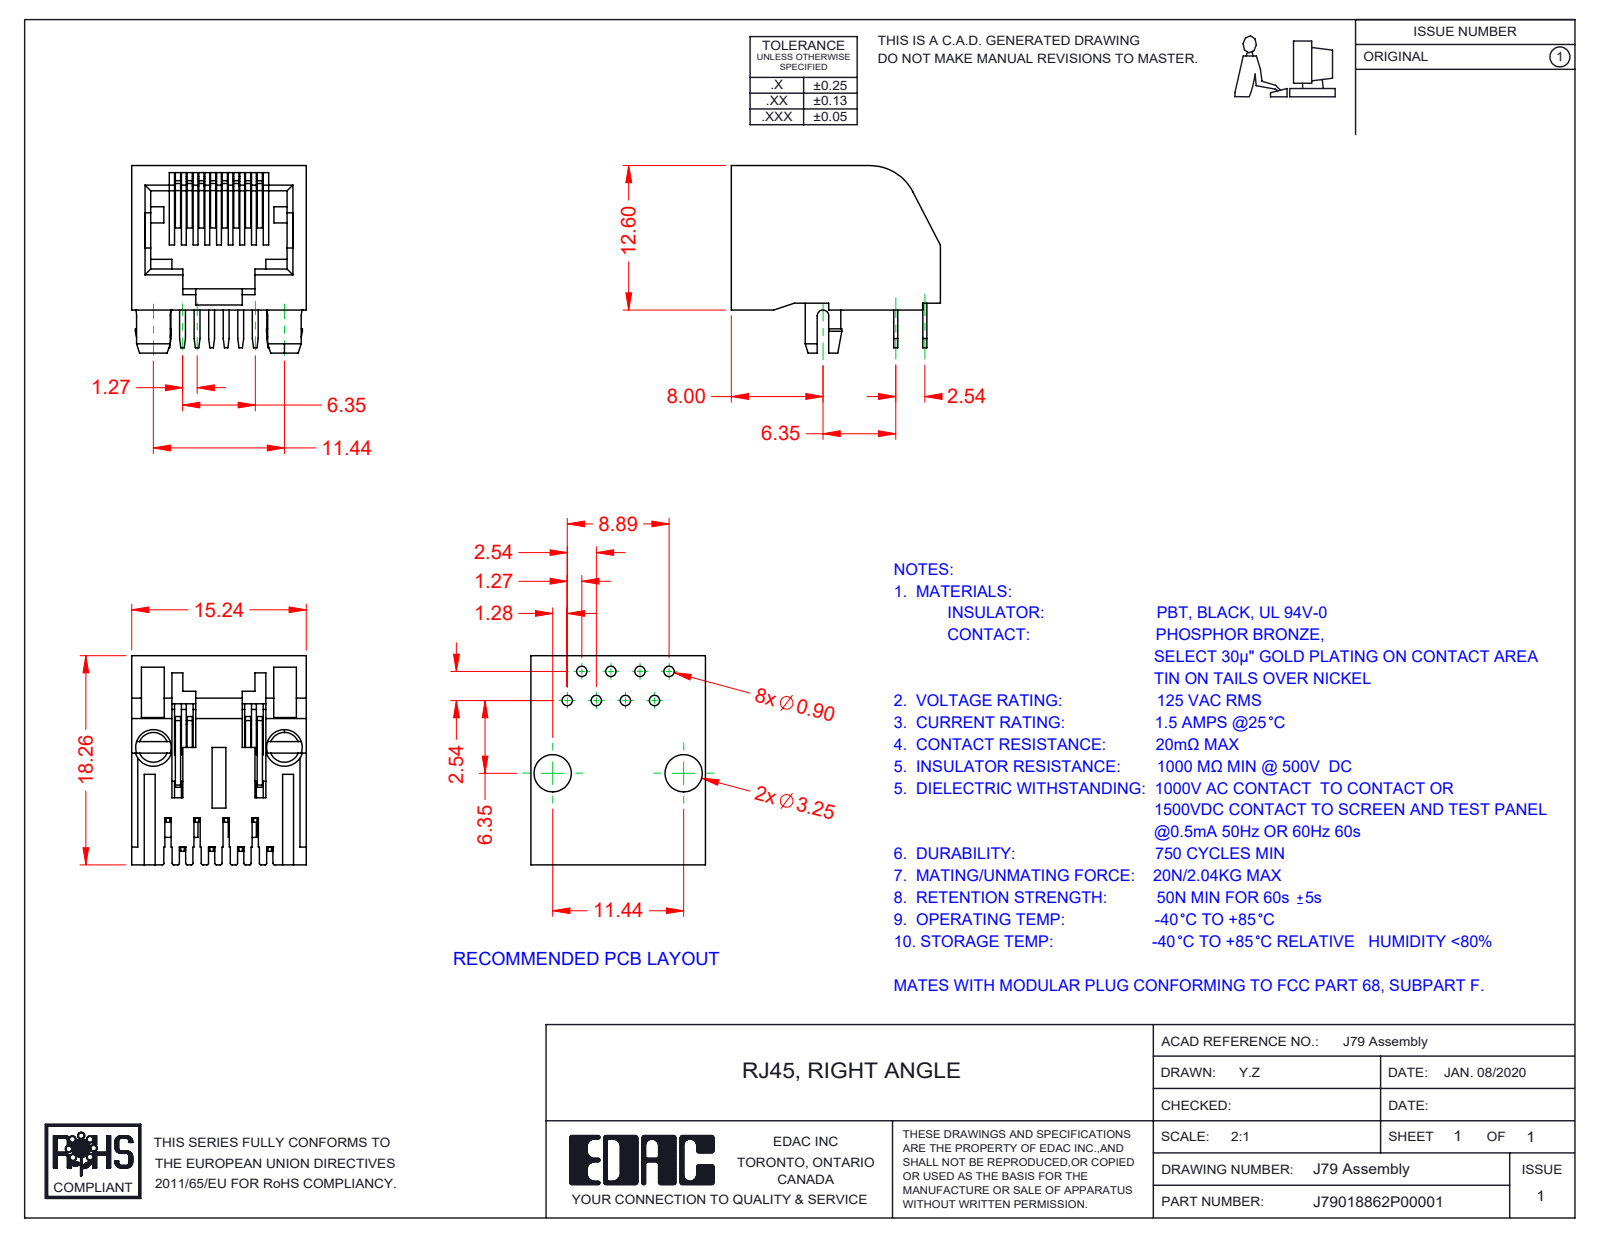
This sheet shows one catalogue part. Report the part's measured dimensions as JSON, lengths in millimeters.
{"part_name": "79 Insulator; RJ79018862P00001; 79 Contacts", "step_written_by": "SolidWorks 2016 (CONFIG_CONTROL_DESIGN)", "units": "millimeters", "bodies": {"solids": 9, "faces": 574, "planar": 424, "cylindrical": 144, "other": 6}, "overall_size": [18.26, 16.36, 15.24], "volume_mm3": 1496, "surface_area_mm2": 3263, "round_bosses_or_shafts": [[3.1, 2]], "partial_cylinders_radius": [[0.15, 16], [0.5, 7], [0.72, 3], [0.36, 2], [1.65, 2], [1.8, 2], [2.16, 2], [0.2, 1]], "face_to_face_distances": [15.24, 2.04, 0.6, 12, 0.36, 4.08, 1.25, 9.8, 2.2, 8.2]}
